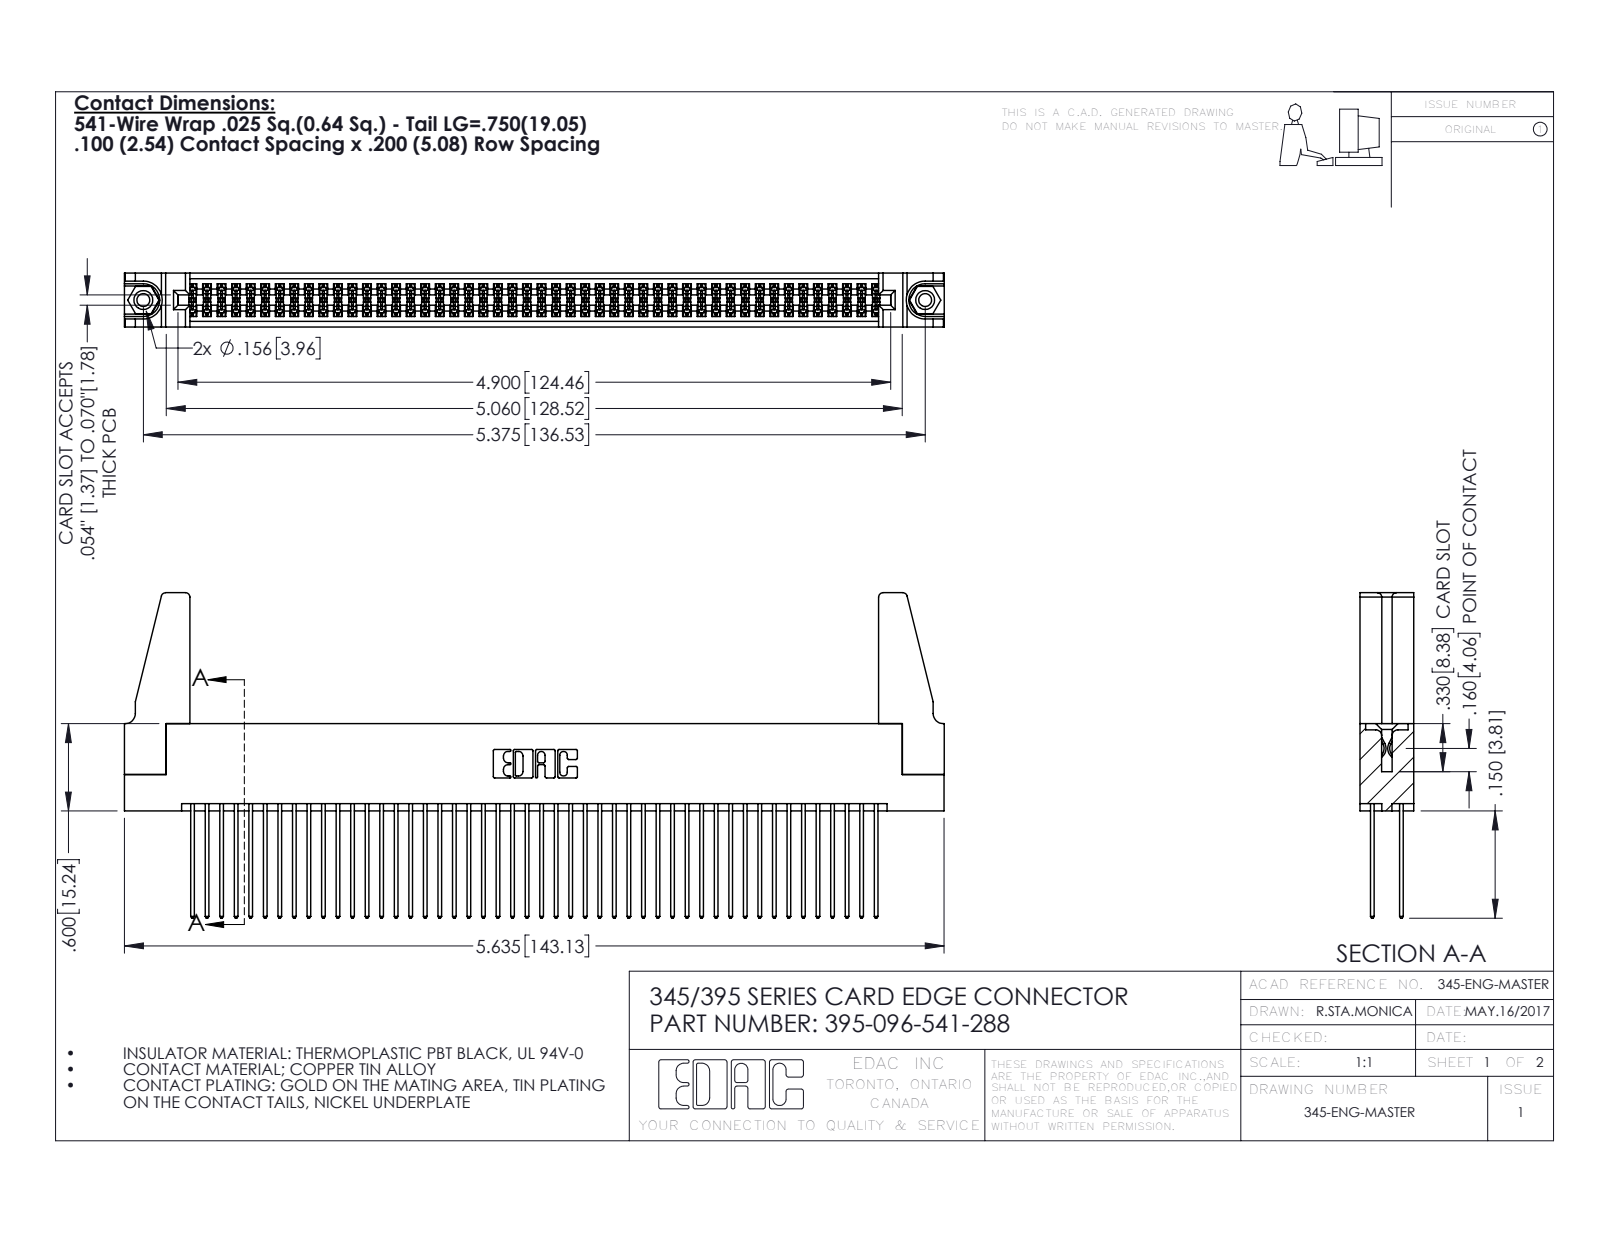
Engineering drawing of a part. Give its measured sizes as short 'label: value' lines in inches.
name: 345-292-001_345-293-141; 345 Part_Flush Mounting Lugs - 0.156 Dia-TH; 345-250-001_345-250-001-102; 395-096-541-288 (+1 more)
written by: SolidWorks 2016 (CONFIG_CONTROL_DESIGN)
unit: in
bodies: 101 solids, 5050 faces (3320 planar, 1714 cylindrical, 16 other)
size: 5.636 × 2.237 × 0.37
volume: 1.084 in³; area: 42.28 in²
holes: 2× ⌀0.089, 2× ⌀0.125, 2× ⌀0.156, 1× ⌀0.064
bosses: 2× ⌀0.155
rounds: 144× R0.006, 96× R0.01, 22× R0.01, 8× R0.03, 6× R0.007, 6× R0.031, 3× R0.026, 2× R0.014
face distances: 0.072, 0.298, 0.2, 0.098, 0.272, 0.025, 0.37, 0.225, 0.175, 0.149
hole spacings: 0.27, 5.139, 5.375
